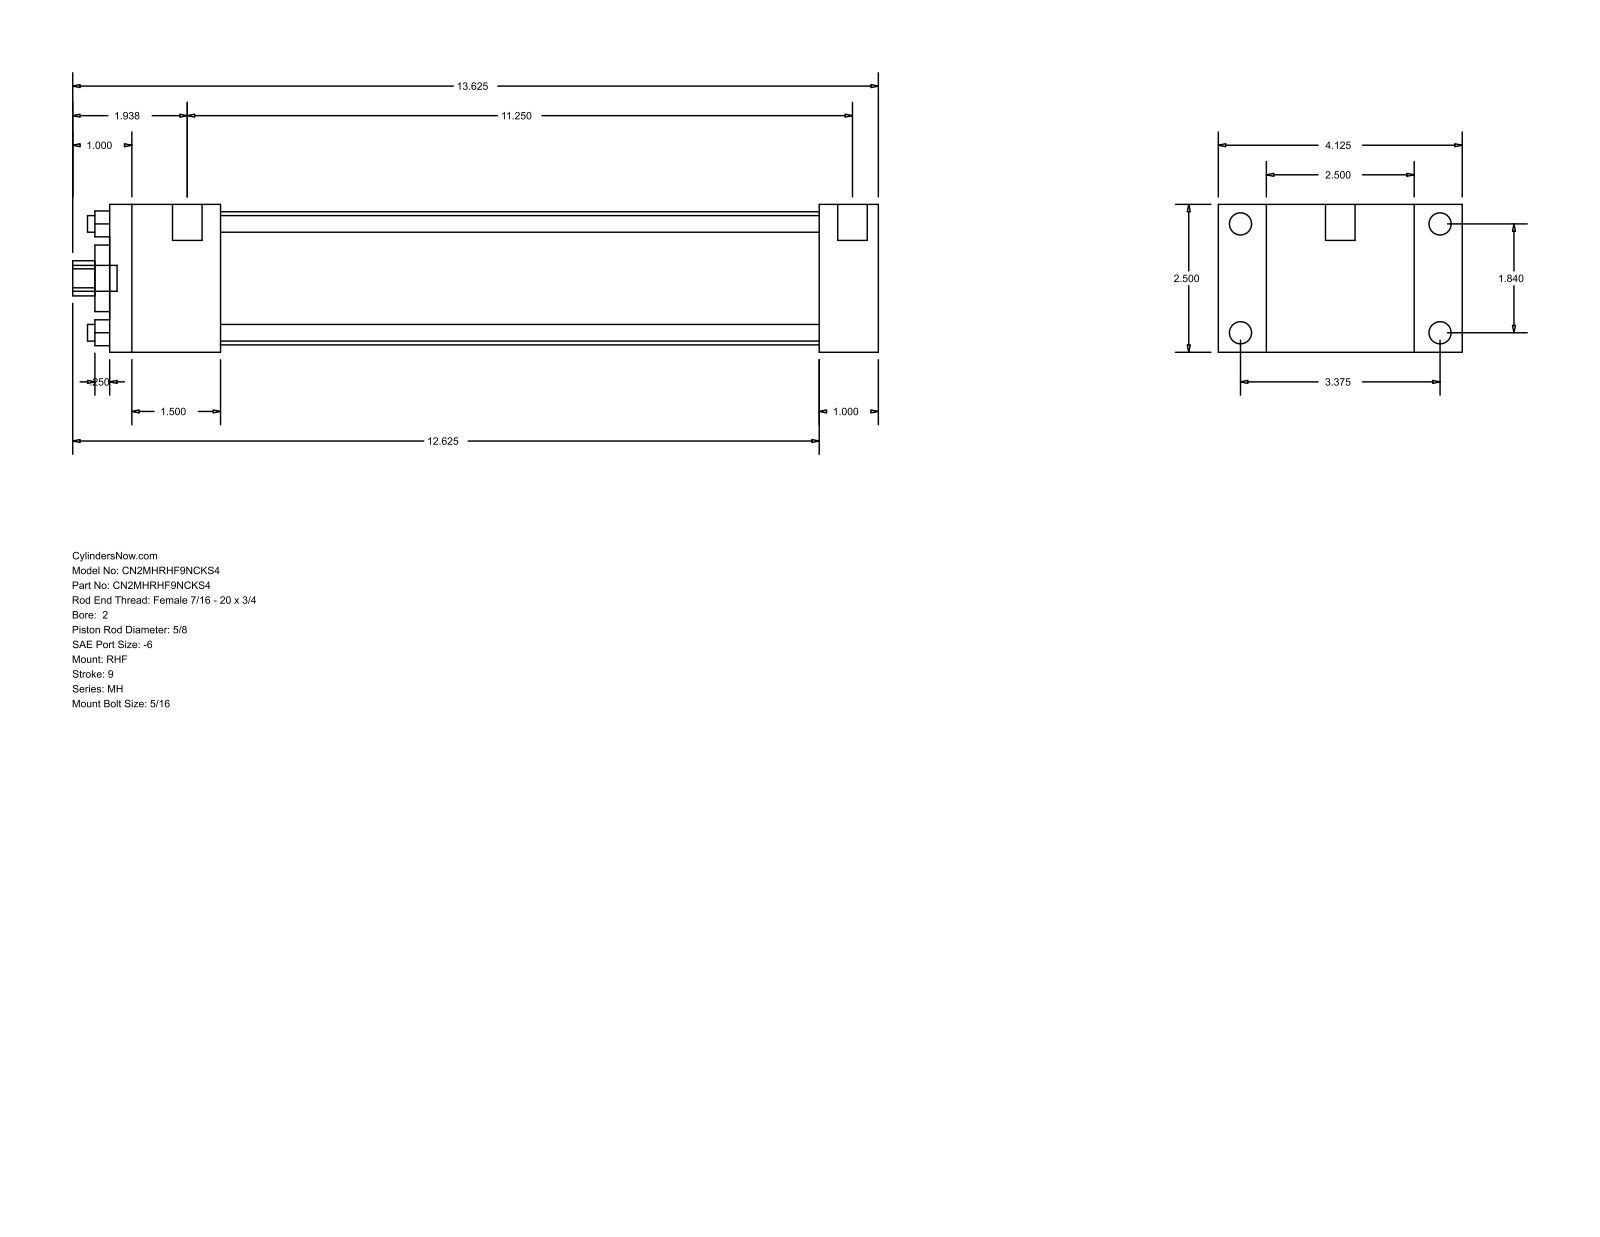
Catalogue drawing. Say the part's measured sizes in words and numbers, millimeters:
The part is named "MH_RHF__0200_0.625". Its 3-D file was written by "GSSL Pune (CONFIG_CONTROL_DESIGN)". It is 0 solids with 88 faces: 60 planar, 28 cylindrical and 0 other. Overall it measures 346.07 by 104.78 by 63.5 millimeters. Round holes: 4 of diameter 7.14, 1 of diameter 15.88, 1 of diameter 28.57, 1 of diameter 57.15. Round bosses or shafts: 4 of diameter 9.53, 4 of diameter 5.56, 2 of diameter 12.7, 1 of diameter 11.11. Partial cylindrical surfaces (rounded edges, fillets, slot ends): 1 of radius 7.54. The main face-to-face distances are 63.5, 25.39, 20.64, 84.14, 304.8, 330.19, 104.78, 47.62, 257.18, 282.57. The hole center spacings are 33.05, 46.74, 66.1.
